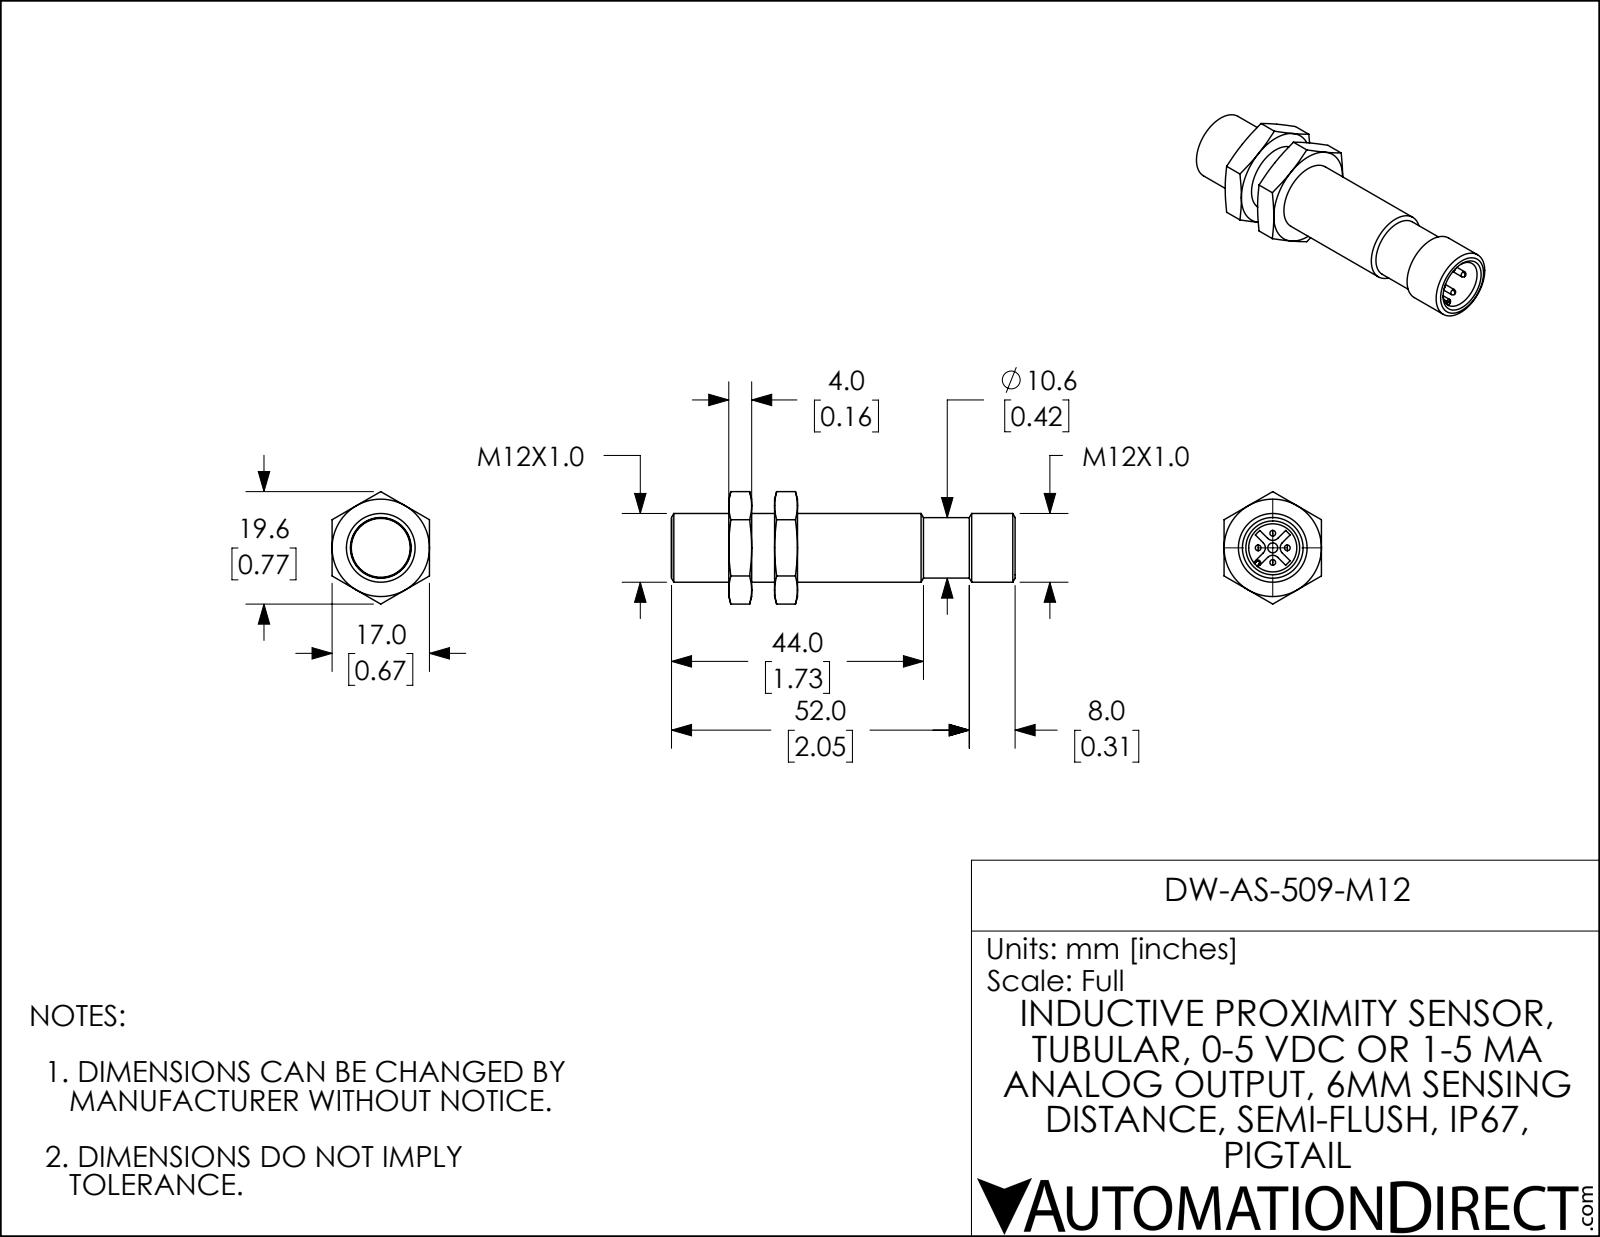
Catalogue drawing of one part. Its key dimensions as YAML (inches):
part_name: "DW-AS-509-M12"
step_written_by: "SolidWorks 2018 (AUTOMOTIVE_DESIGN)"
units: inches
bodies: {solids: 6, faces: 74, planar: 30, cylindrical: 17, other: 27}
overall_size: [2.362, 0.472, 0.472]
volume: 0.159
surface_area: 7.038
round_holes:
  - {diameter: 0.069, count: 1}
  - {diameter: 0.331, count: 1}
  - {diameter: 0.406, count: 1}
round_bosses_or_shafts:
  - {diameter: 0.039, count: 4}
  - {diameter: 0.472, count: 1}
  - {diameter: 0.415, count: 1}
partial_cylinders:
  - {radius: 0.049, count: 4}
  - {radius: 0.008, count: 2}
  - {radius: 0.02, count: 1}
face_to_face_distances: [0.05, 1.887, 1.837, 1.958, 2.008, 0.12, 2.362, 2.312, 0.475, 0.354]
